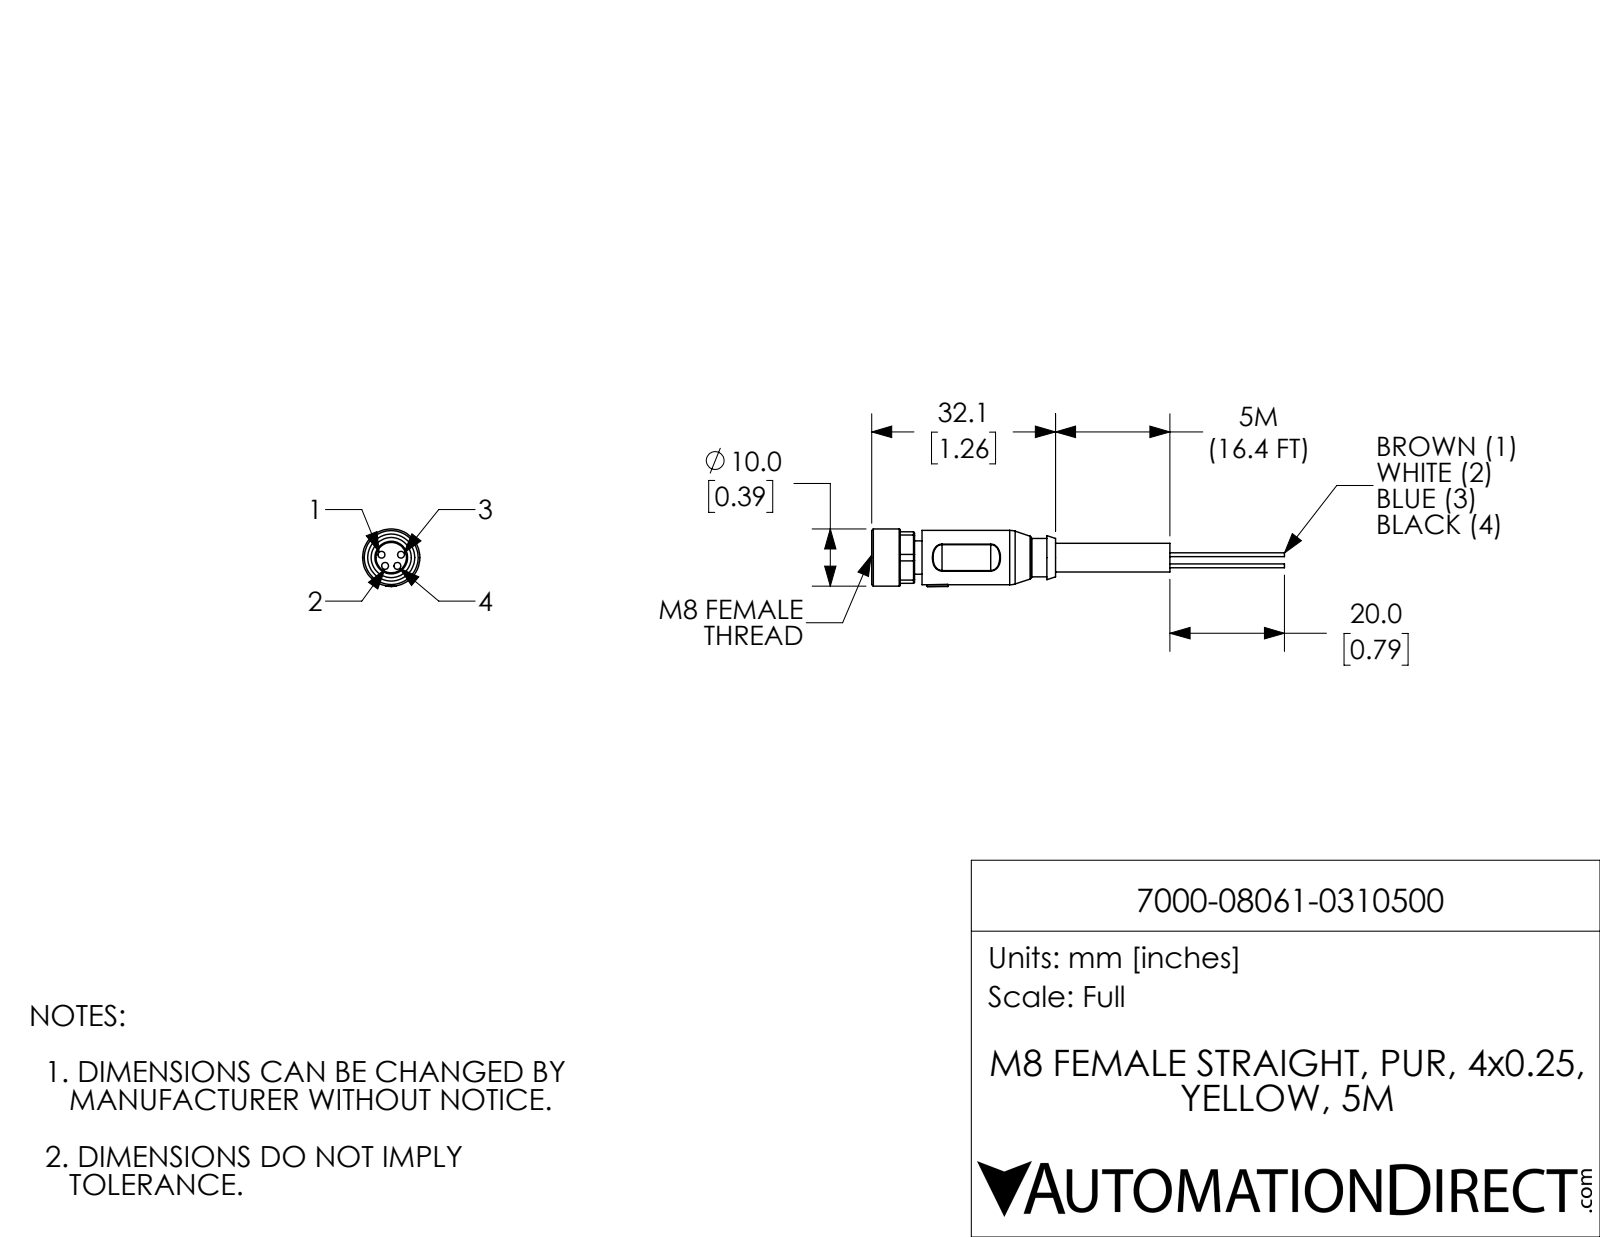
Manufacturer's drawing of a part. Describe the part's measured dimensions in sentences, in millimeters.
The part is named "7000-08061-0310500". Its 3-D file was written by "SolidWorks 2021 (CONFIG_CONTROL_DESIGN)". It is 1 solid with 115 faces: 38 planar, 46 cylindrical and 31 other. Overall it measures 72.1 by 10.1 by 10 millimeters. Its volume is 2 310 cubic millimeters and its surface area 1 899 square millimeters. Round holes: 4 of diameter 1.2, 1 of diameter 7. Round bosses or shafts: 4 of diameter 0.7, 1 of diameter 10, 1 of diameter 9.5, 1 of diameter 6.7, 1 of diameter 5.8, 1 of diameter 5.7, 1 of diameter 5. Partial cylindrical surfaces (rounded edges, fillets, slot ends): 4 of radius 0.2, 4 of radius 2.5, 1 of radius 4.9, 1 of radius 5.1. The main face-to-face distances are 8.3, 1.3, 24.6, 9, 1.5, 0.7, 44.6, 43.3, 6.8, 8.1. The hole center spacings are 1.8, 1.8, 2.1, 3.4, 2.1, 3.4.
